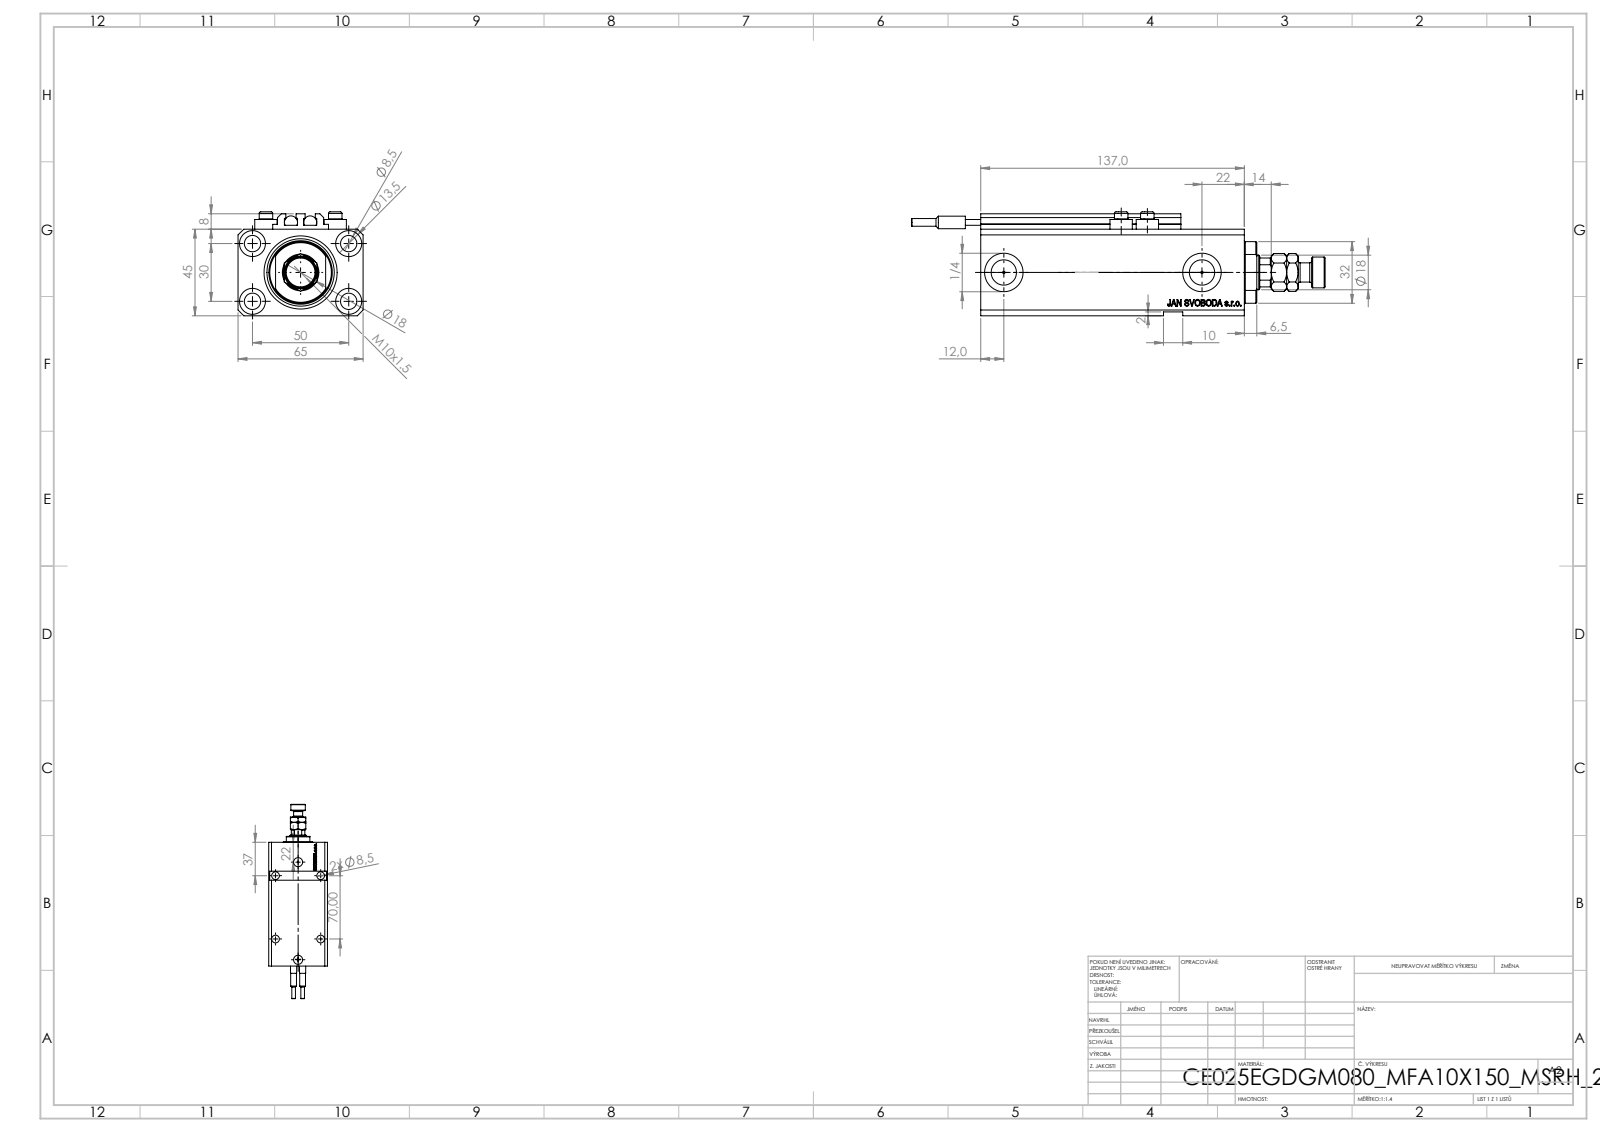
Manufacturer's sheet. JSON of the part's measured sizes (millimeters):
{"part_name": "V250CE_E_Body; SWITCH_V250CE; V250CE_VC_E; V250CE_C_VCP (+2 more)", "step_written_by": "SolidWorks 2019 (CONFIG_CONTROL_DESIGN)", "units": "millimeters", "bodies": {"solids": 11, "faces": 1207, "planar": 563, "cylindrical": 174, "other": 470}, "overall_size": [215, 65, 54], "volume_mm3": 355876, "surface_area_mm2": 99498, "round_holes": [[8.5, 9], [1.25, 4], [4, 4], [13.5, 4], [10, 2], [13.16, 2], [20, 2], [18, 1], [25, 1], [38, 1]], "round_bosses_or_shafts": [[11.6, 4], [7, 4], [6.8, 2], [6.5, 2], [4, 2], [16, 1], [10, 1]], "partial_cylinders_radius": [[0.2, 10], [8.5, 1], [16, 1]], "face_to_face_distances": [45, 65, 47, 2, 14, 2.5, 10, 3, 123, 24], "hole_center_spacings": [29.15, 50, 13.6, 15.12, 27.89, 30, 33.61, 33.62]}
